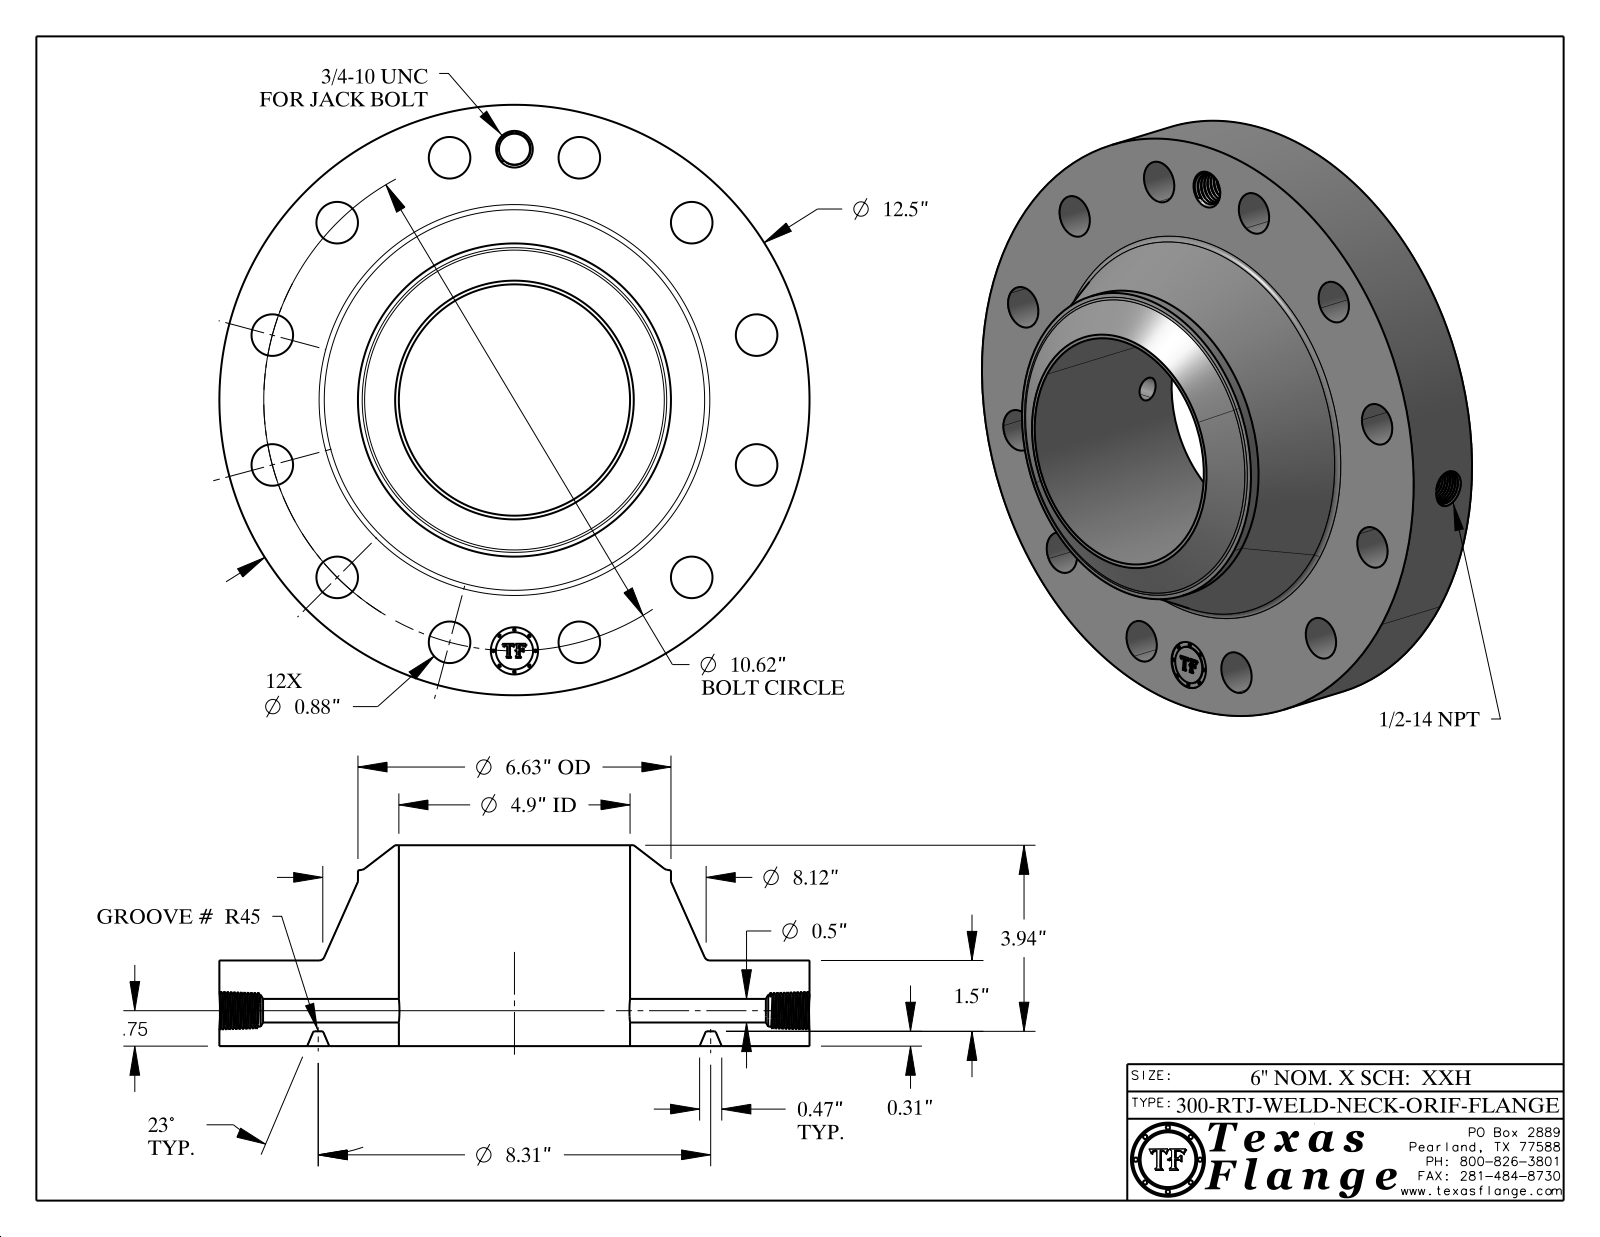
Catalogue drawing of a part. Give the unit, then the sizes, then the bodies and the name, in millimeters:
Units: millimetres
Overall size (bounding box): 317.5 × 317.5 × 108
Round holes (diameter × count): ⌀22.4 ×12, ⌀12.7 ×1, ⌀16.7 ×1, ⌀17.1 ×1, ⌀25.4 ×1, ⌀124.4 ×1
Round bosses / shafts (diameter × count): ⌀1.5 ×8, ⌀317.5 ×1, ⌀168.4 ×1, ⌀20 ×1
Main face-to-face distances: 46.1, 8, 38.1, 108, 100.1, 62, 0.4, 45.7, 37.7, 62.4
Hole centre spacings: 134.9, 190.7, 233.6, 260.6, 134.9, 69.8, 269.7, 35.2
Volume: 3 564 000 mm³ · Surface area: 292 500 mm²
Bodies: 1 solid, 803 faces (370 planar, 104 cylindrical, 329 other)
Part name (STEP PRODUCT): 300-RTJ-WELD-NECK
STEP written by: CATIA V5 STEP AP214 (AUTOMOTIVE_DESIGN)
